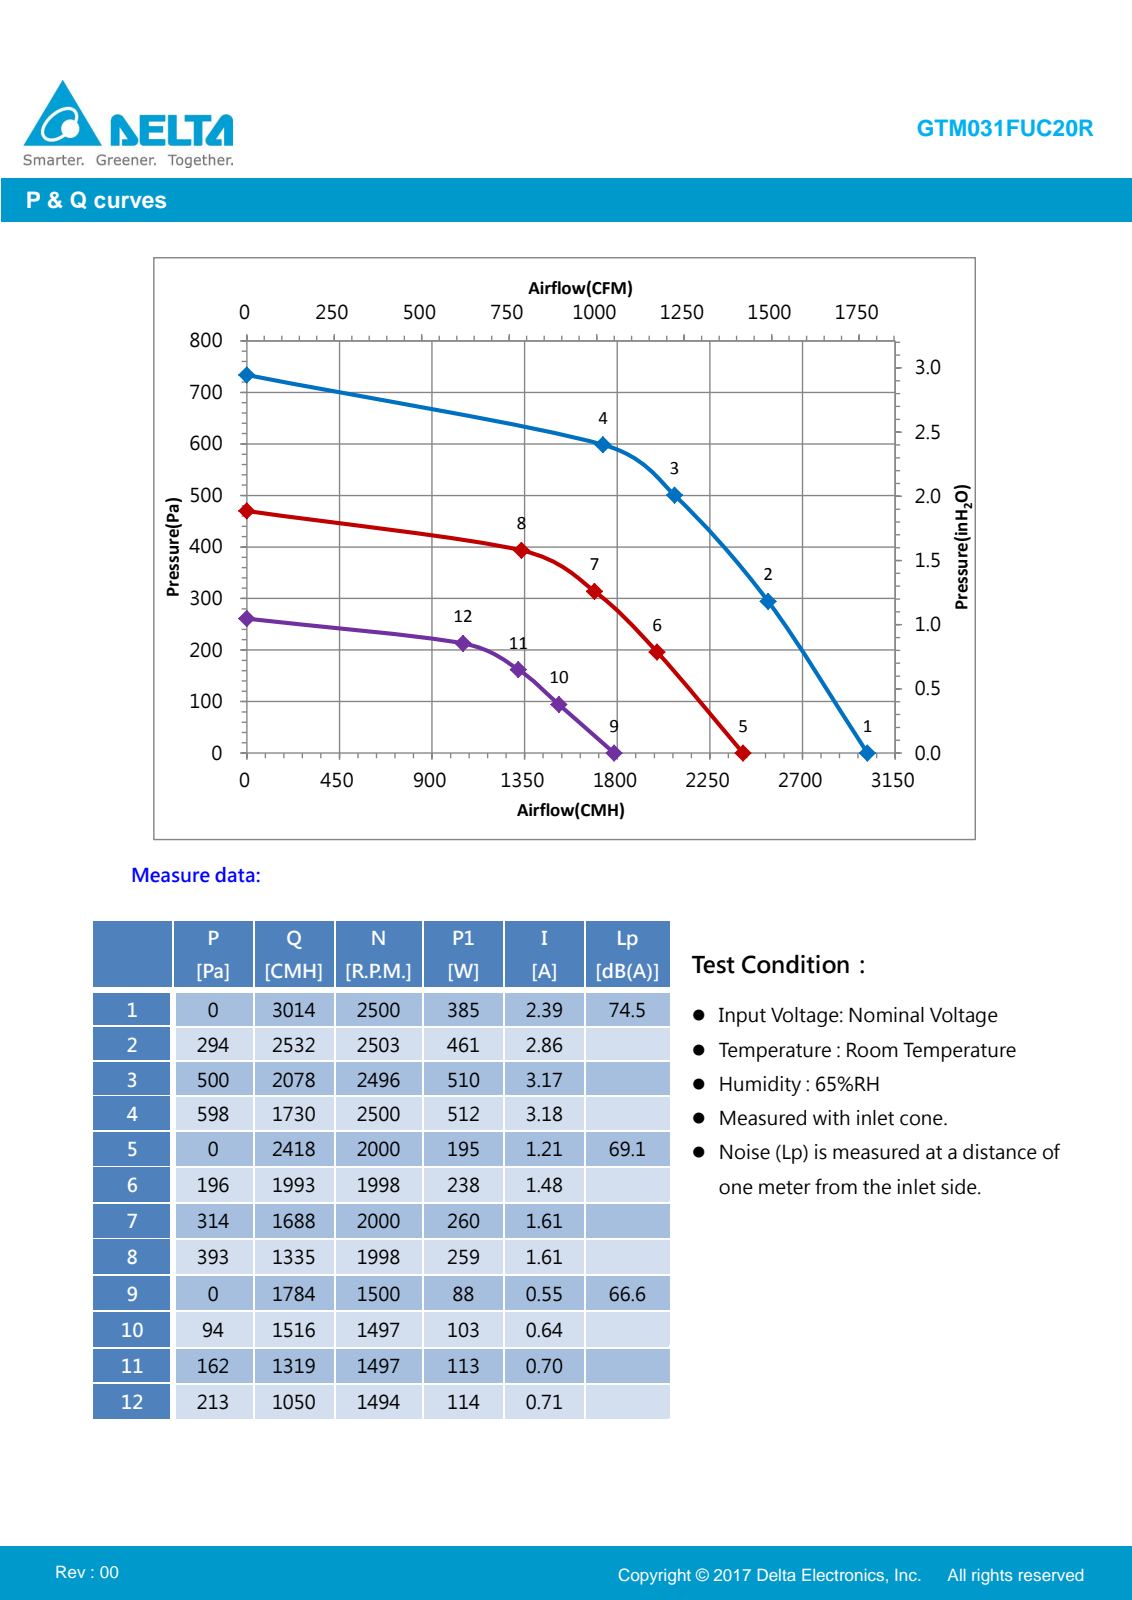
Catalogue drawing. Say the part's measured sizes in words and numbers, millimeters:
The part is named "TOP-PLATE; SUPPORT-2; SUPPORT-22R; BOTTOM-PLATE (+8 more)". Its 3-D file was written by "PRO/ENGINEER BY PARAMETRIC TECHNOLOGY CORPORATION, 2010180 (CONFIG_CONTROL_DESIGN)". It is 68 solids with 4835 faces: 1987 planar, 1230 cylindrical and 1618 other. Overall it measures 400 by 400 by 355.08 millimeters. Its volume is 1 685 000 cubic millimeters and its surface area 1 488 000 square millimeters. Round holes: 12 of diameter 6, 12 of diameter 7, 10 of diameter 6.5, 8 of diameter 3, 8 of diameter 4, 8 of diameter 4.5, 6 of diameter 5, 6 of diameter 5.6, 4 of diameter 2.3, 4 of diameter 2.5, 4 of diameter 11, 3 of diameter 2.8. Round bosses or shafts: 12 of diameter 12, 12 of diameter 11, 8 of diameter 10, 8 of diameter 8, 2 of diameter 14.5, 2 of diameter 9, 1 of diameter 319, 1 of diameter 300. Partial cylindrical surfaces (rounded edges, fillets, slot ends): 161 of radius 0.2, 139 of radius 1, 138 of radius 0.5, 96 of radius 0.6, 28 of radius 2, 24 of radius 0.33, 24 of radius 0.4, 24 of radius 0.84. The main face-to-face distances are 2, 191.2, 189.2, 2.5, 193.2, 166.5, 164.5, 24.7, 26.7, 164. The hole center spacings are 52.8, 55.62, 62.76, 82, 100.44, 113.39, 146.32, 151.51.
